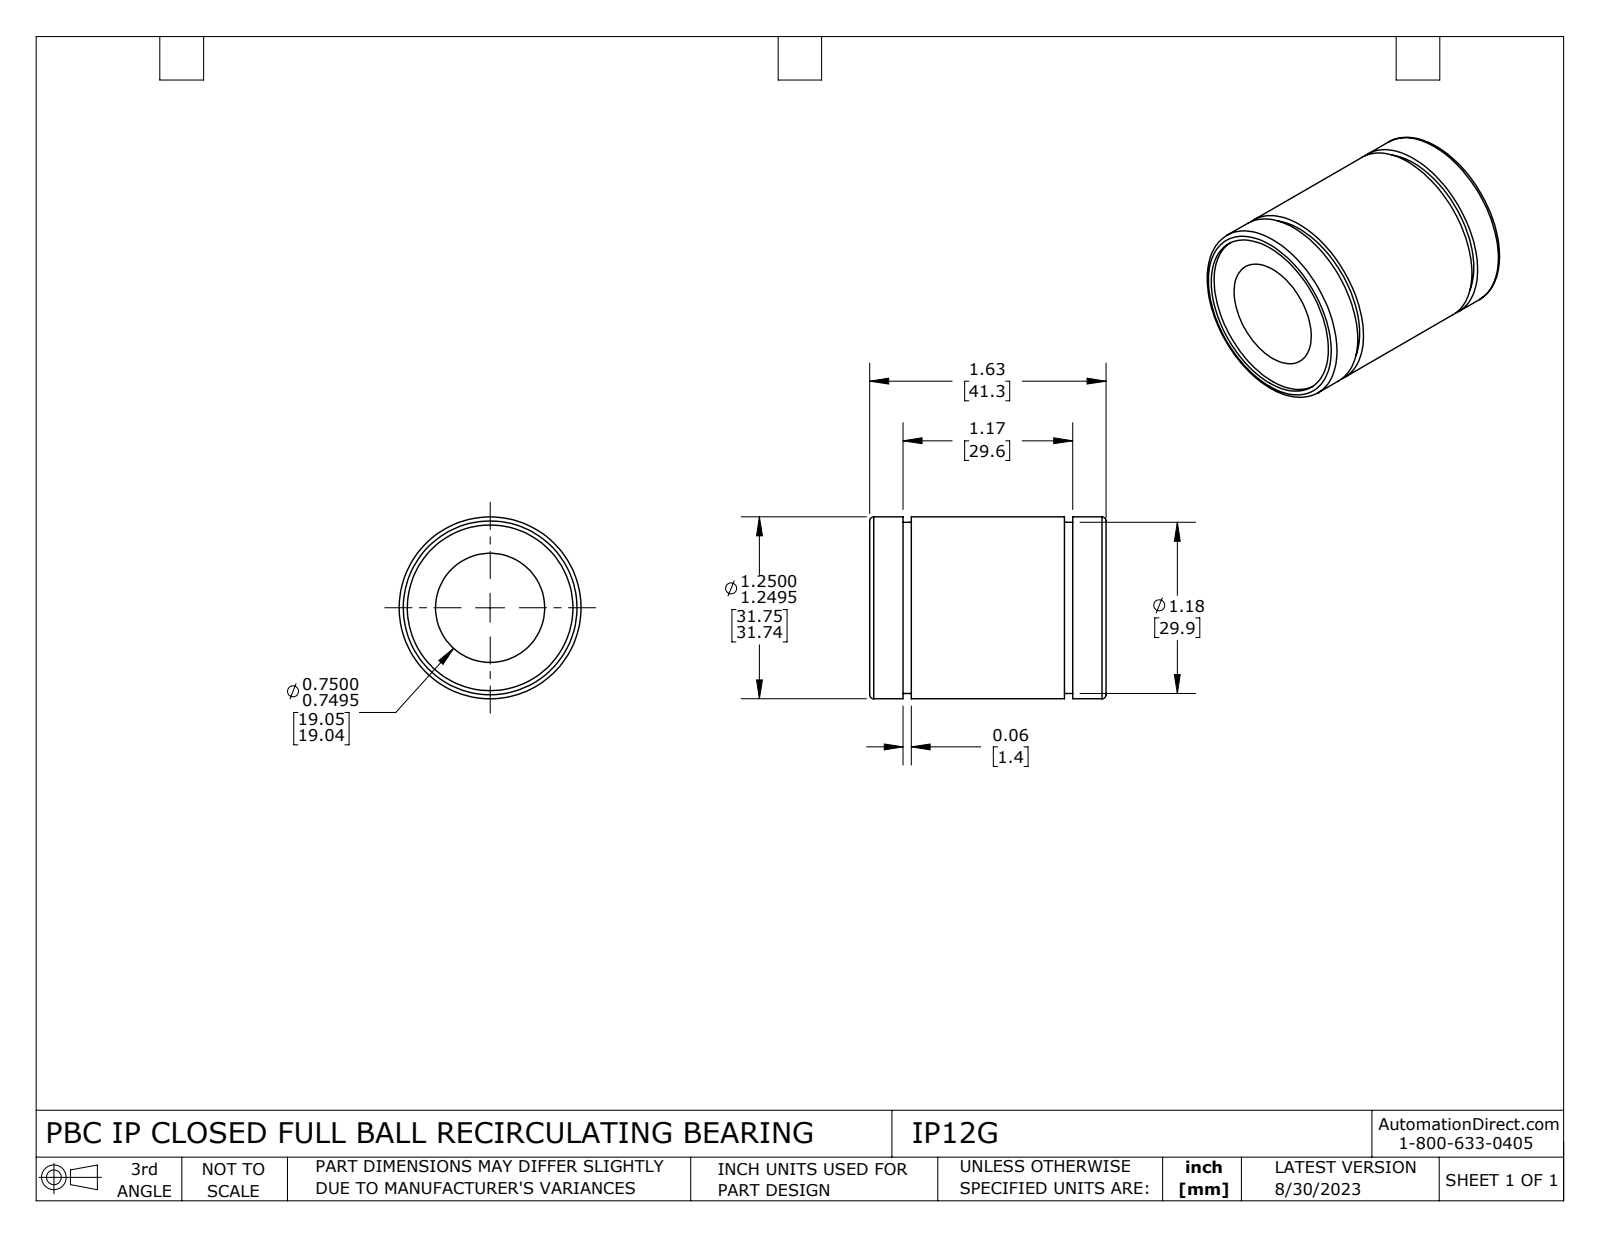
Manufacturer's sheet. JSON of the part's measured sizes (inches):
{"part_name": "IP12G", "step_written_by": "SolidWorks 2021 (CONFIG_CONTROL_DESIGN)", "units": "inches", "bodies": {"solids": 1, "faces": 28, "planar": 8, "cylindrical": 16, "other": 4}, "overall_size": [1.625, 1.25, 1.25], "volume_in3": 1.227, "surface_area_in2": 12.29, "round_holes": [[0.75, 1], [1.138, 1]], "round_bosses_or_shafts": [[1.25, 1], [1.176, 1]], "face_to_face_distances": [1.569, 0.202, 0.258, 1.311, 1.367, 0.056, 1.109, 0.028, 0.23, 0.286]}
